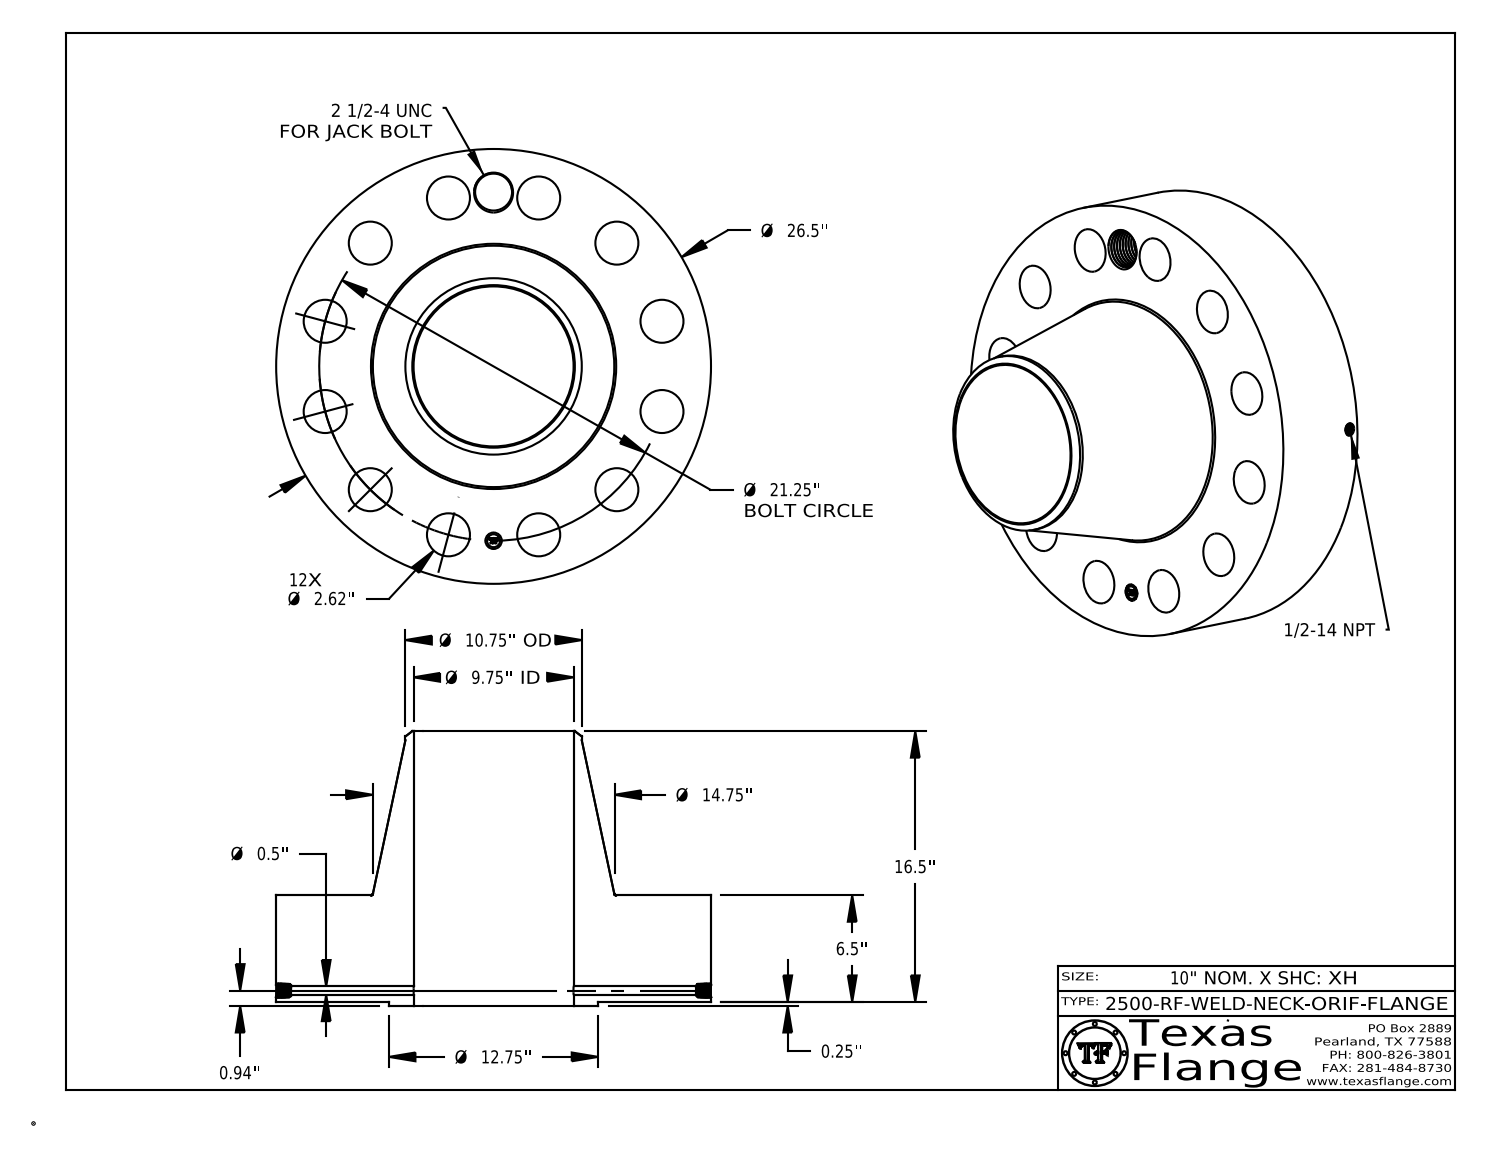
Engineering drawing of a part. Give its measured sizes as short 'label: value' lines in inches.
name: 2500-RF-WELD-NECK
written by: CATIA V5 STEP AP214 (AUTOMOTIVE_DESIGN)
unit: in
bodies: 1 solid, 843 faces (369 planar, 124 cylindrical, 350 other)
size: 26.5 × 26.5 × 16.75
volume: 3 177 in³; area: 2 937 in²
holes: 12× ⌀2.62, 1× ⌀0.5, 1× ⌀0.672, 1× ⌀1, 1× ⌀2.25, 1× ⌀9.75
bosses: 8× ⌀0.061, 1× ⌀26.5, 1× ⌀12.75, 1× ⌀10.75, 1× ⌀0.788
face distances: 6.5, 0.25, 6.75, 16.75, 16.5, 10, 0.015, 6.735, 6.485, 10.015
hole spacings: 10.625, 5.5, 15.026, 18.403, 20.526, 10.625, 21.25, 2.774
